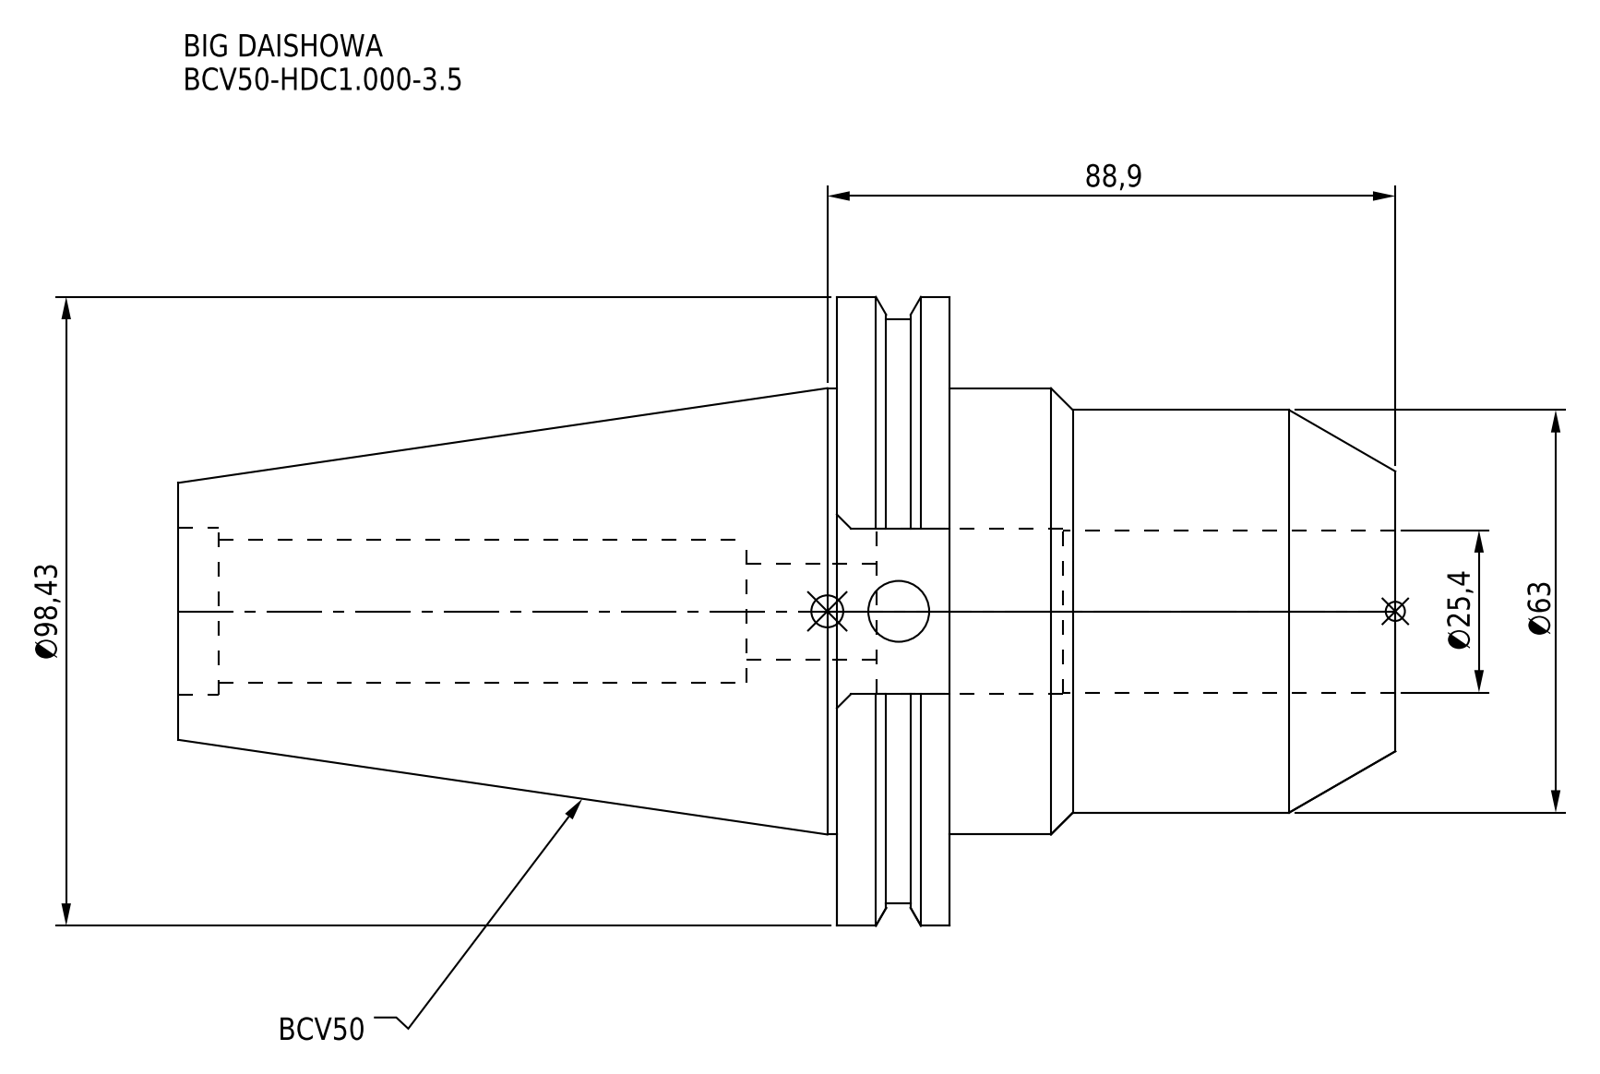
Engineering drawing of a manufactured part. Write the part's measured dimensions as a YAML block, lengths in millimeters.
part_name: "BCV50-HDC1_000-3_5"
step_written_by: "CREO PARAMETRIC BY PTC INC, 2016380 (AUTOMOTIVE_DESIGN)"
units: millimeters
bodies: {solids: 1, faces: 59, planar: 23, cylindrical: 26, other: 10}
overall_size: [190.5, 98.42, 94.95]
volume: 506263
surface_area: 62184
round_holes:
  - {diameter: 9.53, count: 1}
  - {diameter: 15, count: 1}
  - {diameter: 22.3, count: 1}
  - {diameter: 25.4, count: 1}
  - {diameter: 25.9, count: 1}
  - {diameter: 26.23, count: 1}
round_bosses_or_shafts:
  - {diameter: 98.42, count: 1}
  - {diameter: 91.29, count: 1}
  - {diameter: 69.85, count: 1}
  - {diameter: 63, count: 1}
face_to_face_distances: [17.55, 69.85, 87.4, 190.5, 120.65, 103.1, 72.95, 81.2, 11.35, 6.2]
